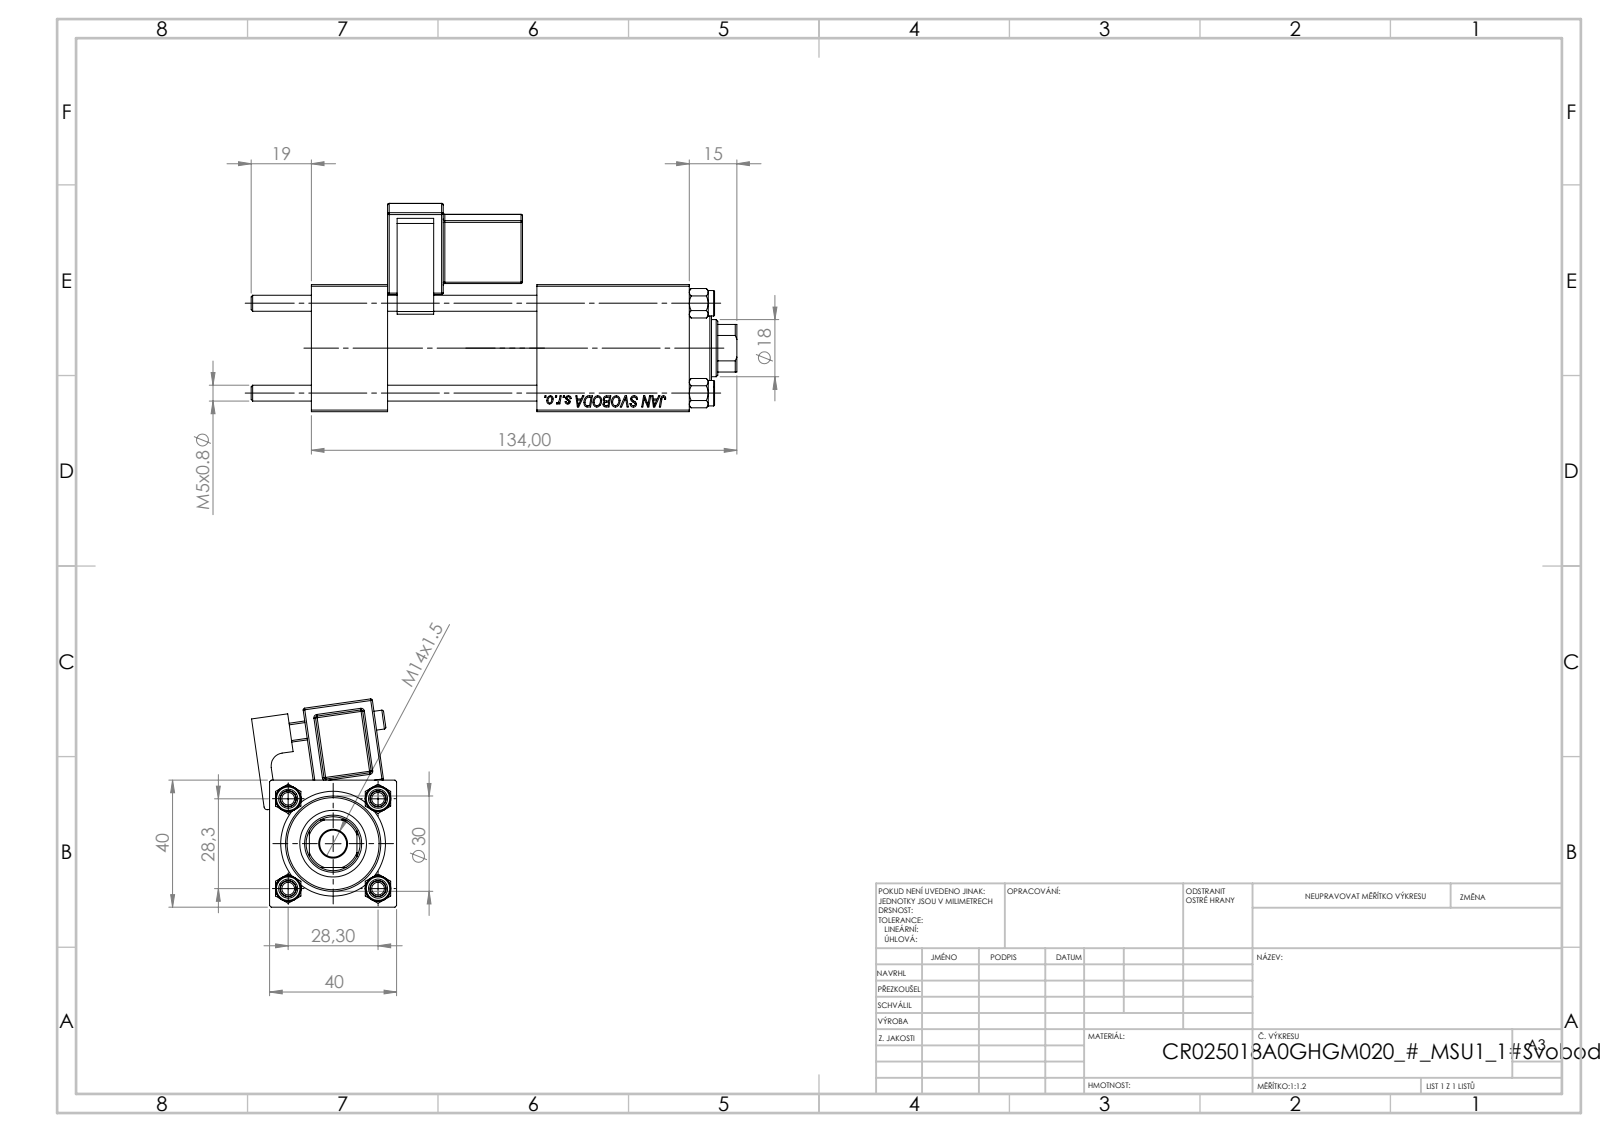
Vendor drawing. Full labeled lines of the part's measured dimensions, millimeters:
Part name (STEP PRODUCT): NUT_M5; V215_VC_A; V215CR_VCP; V215CR_BODY_A (+2 more)
STEP written by: SolidWorks 2019 (CONFIG_CONTROL_DESIGN)
Units: millimetres
Bodies: 12 solids, 1207 faces (547 planar, 106 cylindrical, 554 other)
Overall size (bounding box): 153 × 65.59 × 45.69
Volume: 172 714 mm³ · Surface area: 67 126 mm²
Round holes (diameter × count): ⌀5 ×4, ⌀20 ×3, ⌀7 ×2, ⌀13.16 ×2, ⌀8.5 ×1, ⌀18 ×1, ⌀21 ×1, ⌀25 ×1, ⌀30 ×1
Round bosses / shafts (diameter × count): ⌀8 ×4, ⌀31 ×1, ⌀6 ×1
Partial cylindrical surfaces — rounded edges, fillets, slot ends (radius × count): R0.5 ×24, R1 ×1, R2.5 ×1, R4 ×1, R8.5 ×1
Main face-to-face distances: 40, 24, 3, 71, 47, 90.3, 66.3, 19.3, 119, 95
Hole centre spacings: 20.01, 28.3, 40.02, 72
